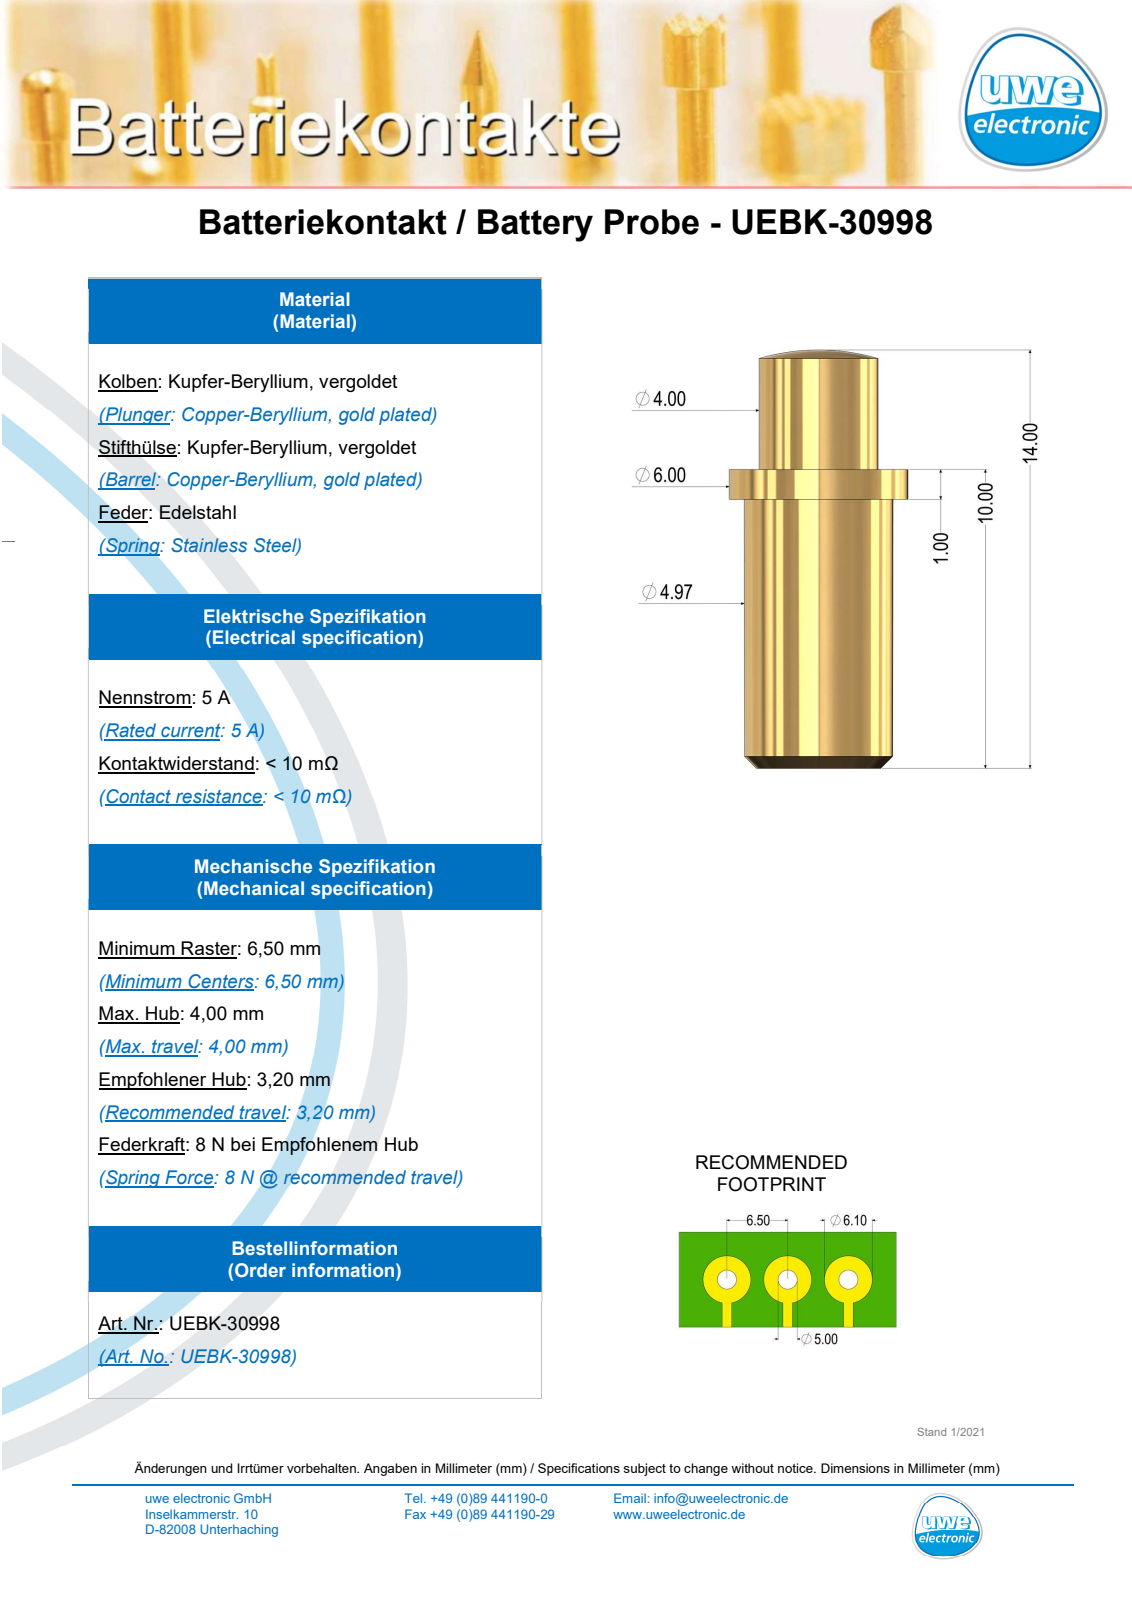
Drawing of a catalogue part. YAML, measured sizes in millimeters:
part_name: "UEBK-30998_2017_11_28"
step_written_by: "SolidWorks 2017 (AUTOMOTIVE_DESIGN)"
units: millimeters
bodies: {solids: 1, faces: 13, planar: 3, cylindrical: 4, other: 6}
overall_size: [14, 6, 6]
volume: 251
surface_area: 259
round_bosses_or_shafts:
  - {diameter: 6, count: 1}
  - {diameter: 3.99, count: 1}
face_to_face_distances: [10, 1, 9]
